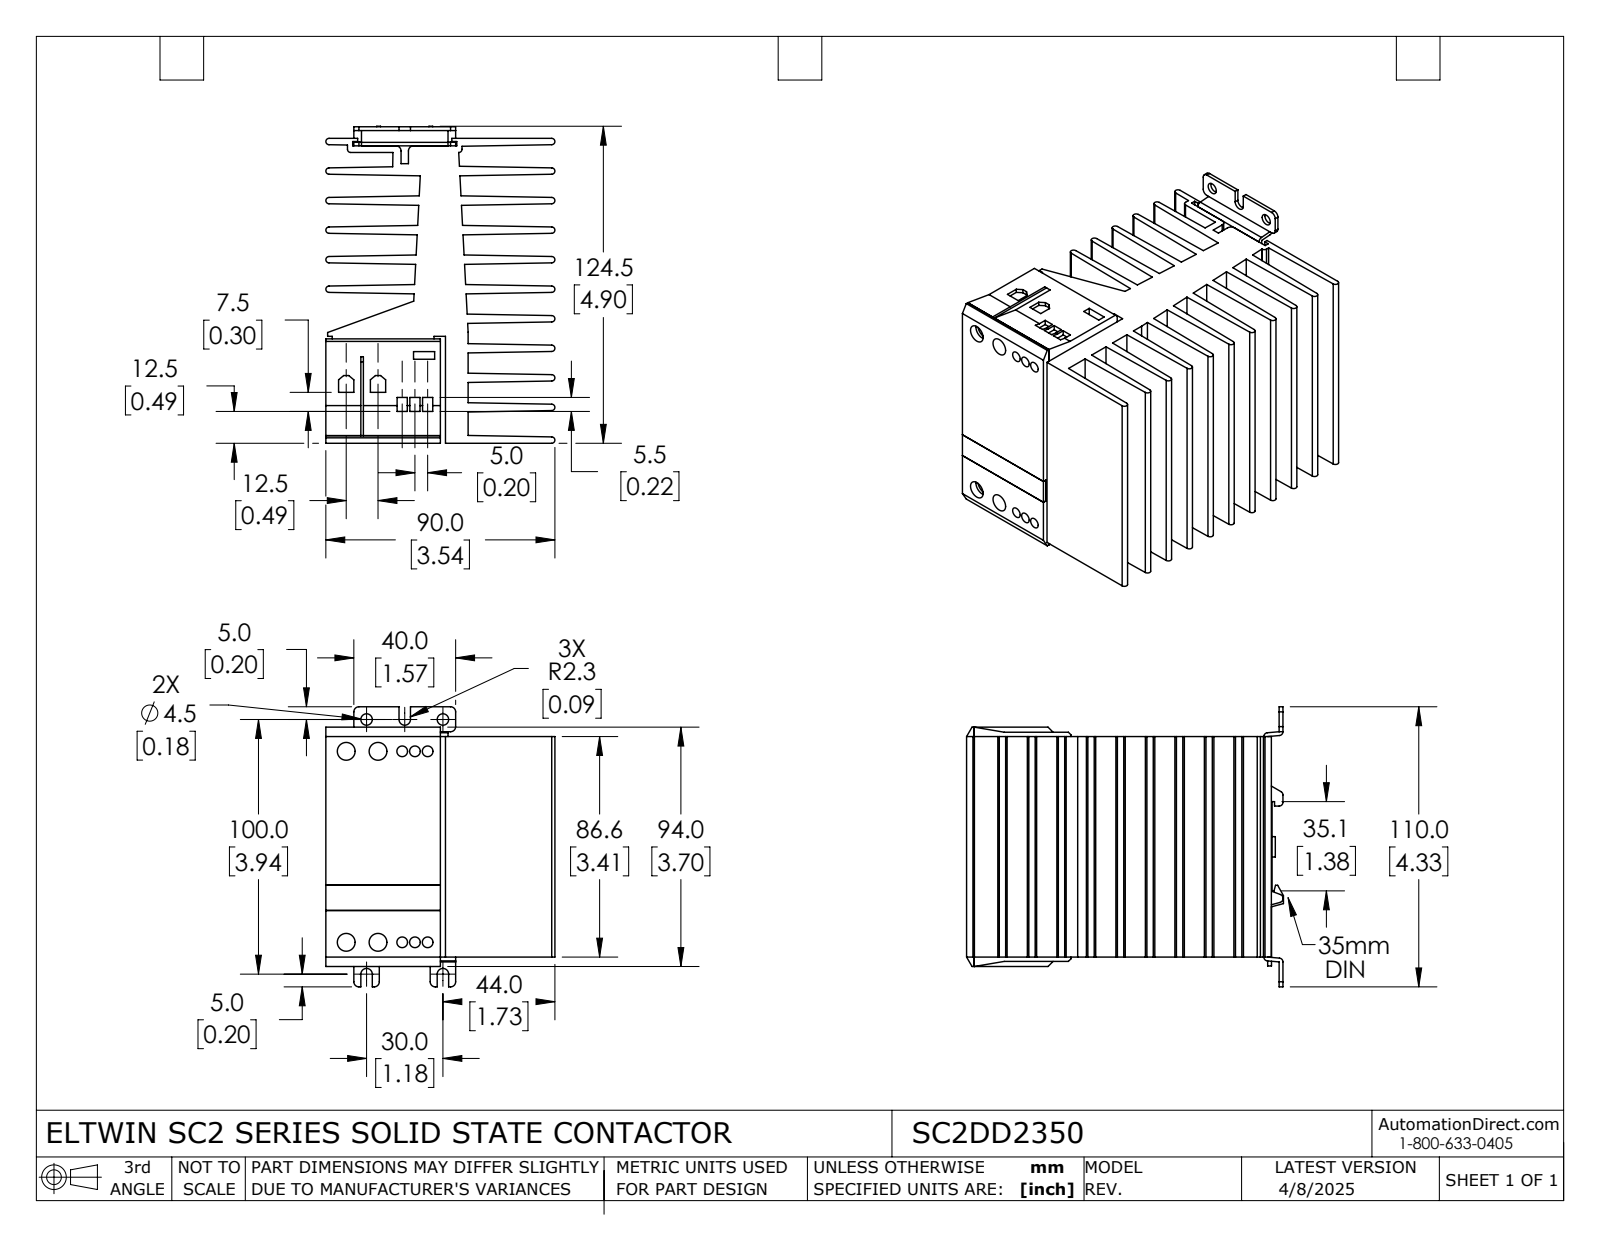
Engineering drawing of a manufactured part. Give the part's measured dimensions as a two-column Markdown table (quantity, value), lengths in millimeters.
| quantity | value |
| --- | --- |
| part name | SC2DD2350 |
| STEP written by | SolidWorks 2021 (AUTOMOTIVE_DESIGN) |
| units | millimeters |
| bodies | 7 solids, 404 faces (294 planar, 110 cylindrical, 0 other) |
| overall size | 124.5 × 110 × 90 |
| volume | 511 300 mm³ |
| surface area | 179 000 mm² |
| round holes (diameter × count) | 4.2 × 6, 4.4 × 6, 7 × 4, 4.5 × 2, 8 × 2 |
| round bosses / shafts (diameter × count) | 8 × 3 |
| partial cylindrical surfaces (radius × count) | 1.2 × 19, 2 × 18, 1.5 × 10, 1.3 × 4, 2.3 × 3 |
| main face-to-face distances | 11.6, 23.2, 34.8, 4, 7.6, 4, 46.4, 42.4, 46.4, 54 |
| hole center spacings | 75, 5, 75.2, 9.5, 10, 12.5, 14.5, 19.5 |
